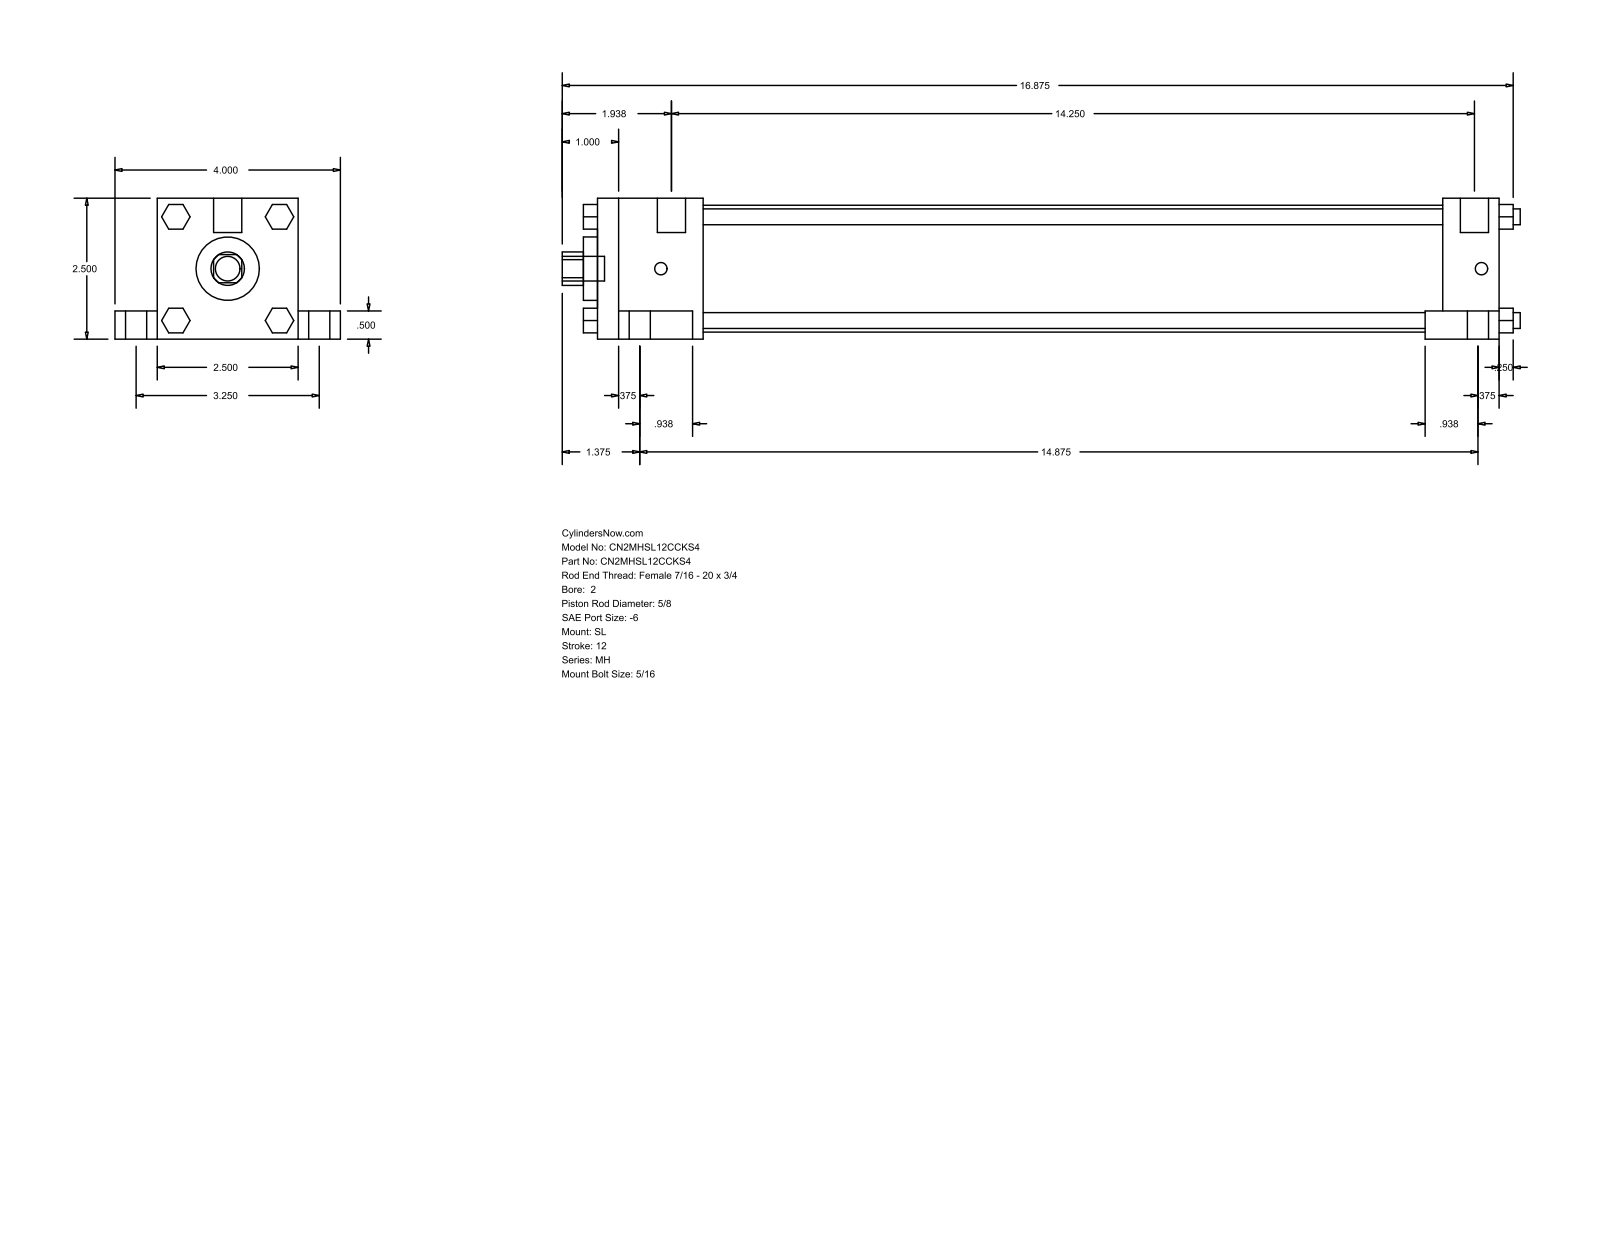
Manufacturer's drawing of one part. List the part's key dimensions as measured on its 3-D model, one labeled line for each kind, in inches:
Part name (STEP PRODUCT): MH_SL__0200_0.625
STEP written by: GSSL Pune (CONFIG_CONTROL_DESIGN)
Units: inches
Bodies: 0 solids, 148 faces (112 planar, 36 cylindrical, 0 other)
Overall size (bounding box): 17 × 4 × 2.5
Round holes (diameter × count): ⌀0.625 ×1, ⌀1.125 ×1, ⌀2.25 ×1
Round bosses / shafts (diameter × count): ⌀0.625 ×4, ⌀0.375 ×4, ⌀0.281 ×4, ⌀0.219 ×4, ⌀0.5 ×2, ⌀0.437 ×1
Partial cylindrical surfaces — rounded edges, fillets, slot ends (radius × count): R0.297 ×1
Main face-to-face distances: 2.5, 16, 0.5, 0.75, 2, 3.25, 15, 1, 1.875, 13.125
